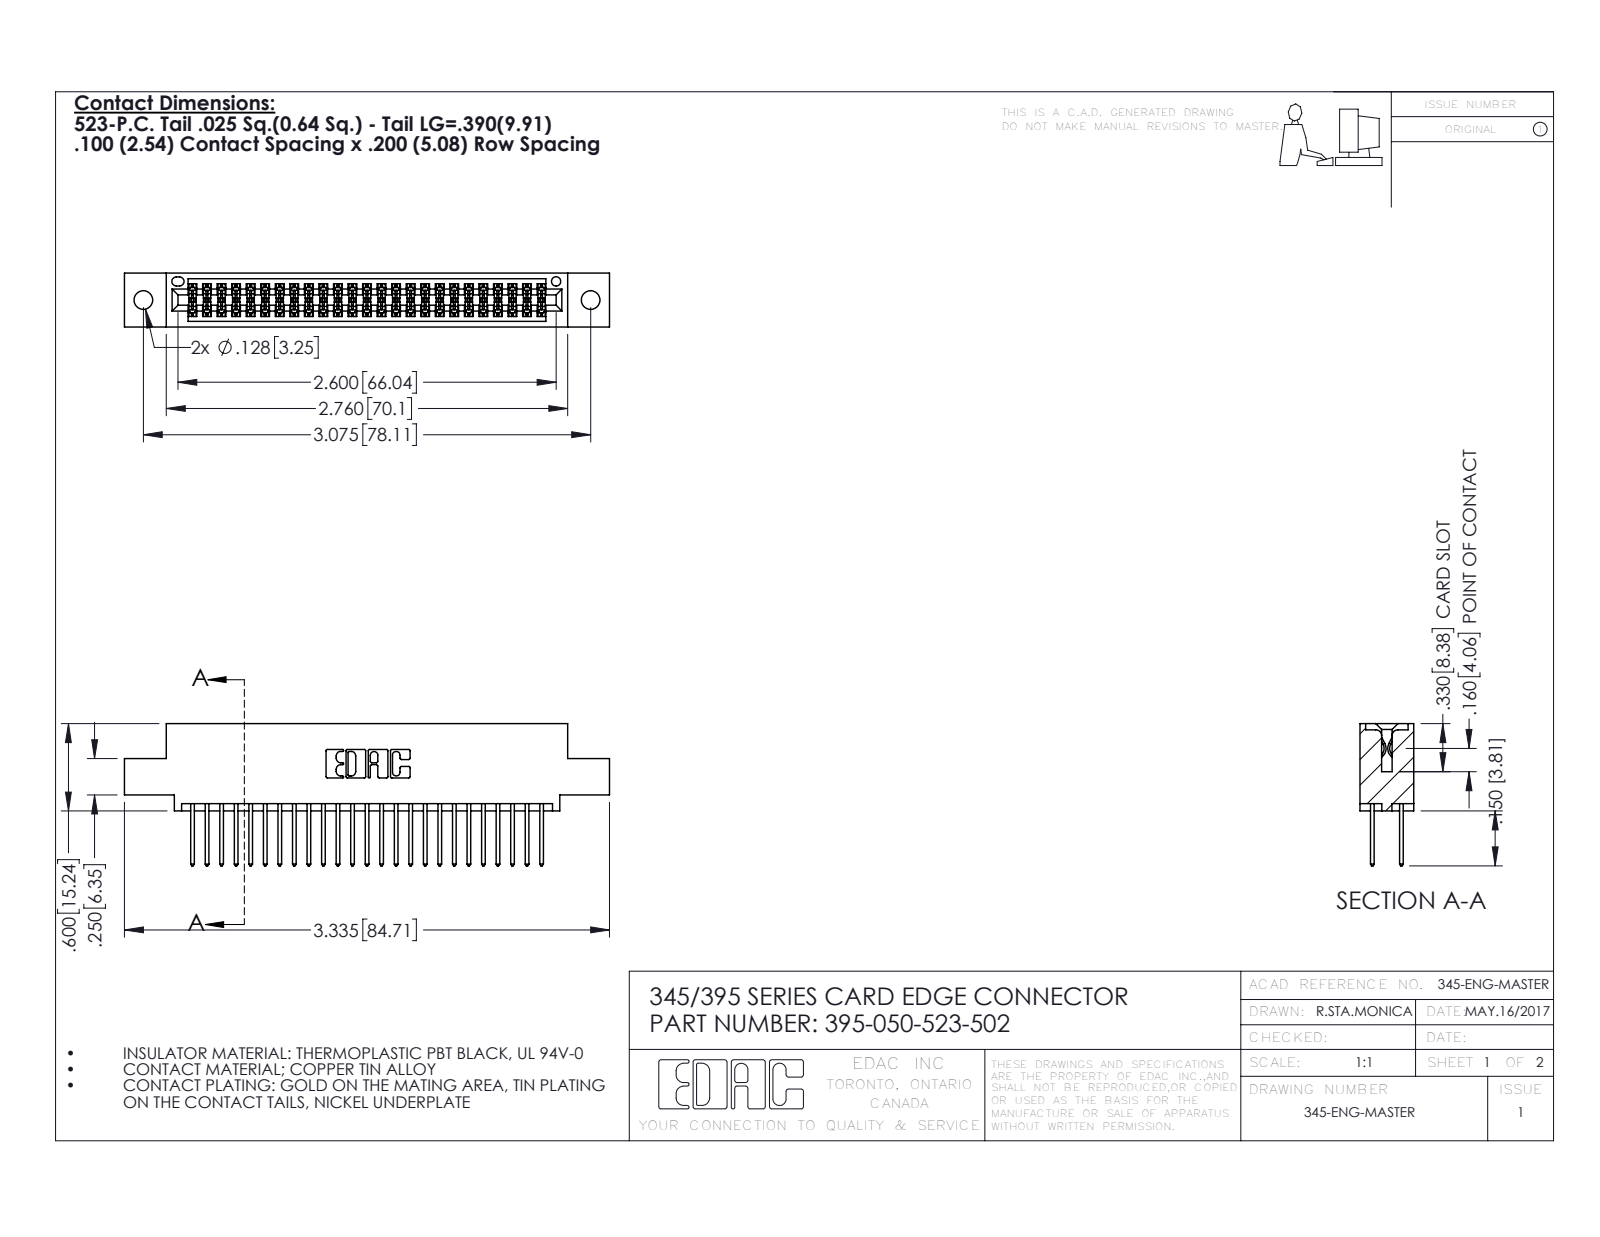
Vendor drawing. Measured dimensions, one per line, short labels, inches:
name: 345-292-001_345-293-123; 395-050-523-502; 345 Part_0.110 Offset - 0.128 Dia
written by: SolidWorks 2016 (CONFIG_CONTROL_DESIGN)
unit: in
bodies: 51 solids, 2630 faces (1734 planar, 896 cylindrical, 0 other)
size: 3.335 × 0.977 × 0.37
volume: 0.492 in³; area: 18.4 in²
holes: 2× ⌀0.128, 1× ⌀0.064
rounds: 75× R0.006, 50× R0.01, 22× R0.01, 6× R0.007, 6× R0.031, 3× R0.026, 2× R0.014, 2× R0.019
face distances: 0.298, 0.072, 0.2, 0.098, 0.272, 0.025, 0.37, 0.225, 0.175, 0.149
hole spacings: 0.27, 2.84, 3.075
